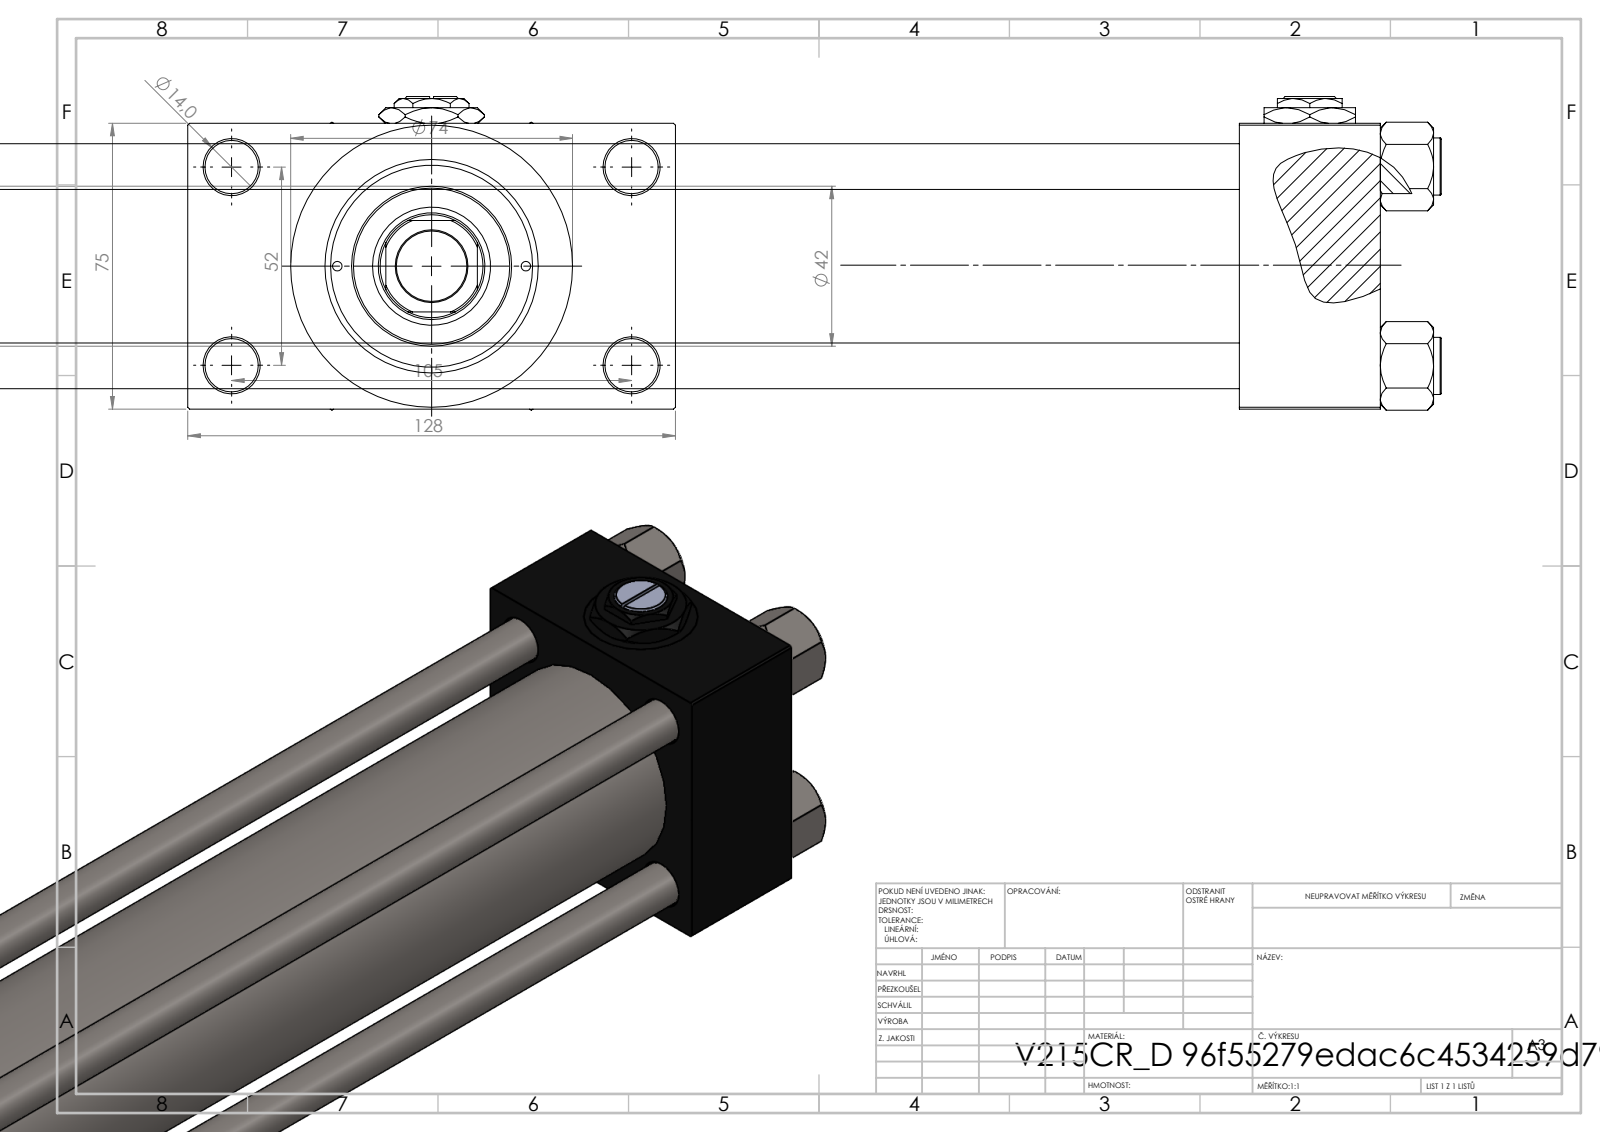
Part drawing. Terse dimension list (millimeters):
name: V215CR_VCP_D; NUT_M5_D; V215_VC_A; Zatka_pro_OIL_PORT (+2 more)
written by: SolidWorks 2019 (CONFIG_CONTROL_DESIGN)
unit: mm
bodies: 13 solids, 1212 faces (547 planar, 103 cylindrical, 562 other)
size: 575 × 128 × 82.27
volume: 1 397 000 mm³; area: 392 050 mm²
holes: 4× ⌀12, 4× ⌀14, 4× ⌀20.96, 4× ⌀30, 3× ⌀7, 2× ⌀2.5, 1× ⌀18.5, 1× ⌀28, 1× ⌀31, 1× ⌀41, 1× ⌀50, 1× ⌀53
bosses: 4× ⌀15, 1× ⌀74, 1× ⌀56, 1× ⌀42
rounds: 1× R13.5
face distances: 75, 438, 37, 475, 26.5, 518, 481, 43, 101.5, 16
hole spacings: 26.19, 26.35, 36.98, 38.03, 52.3, 57.22, 58.43, 58.59
